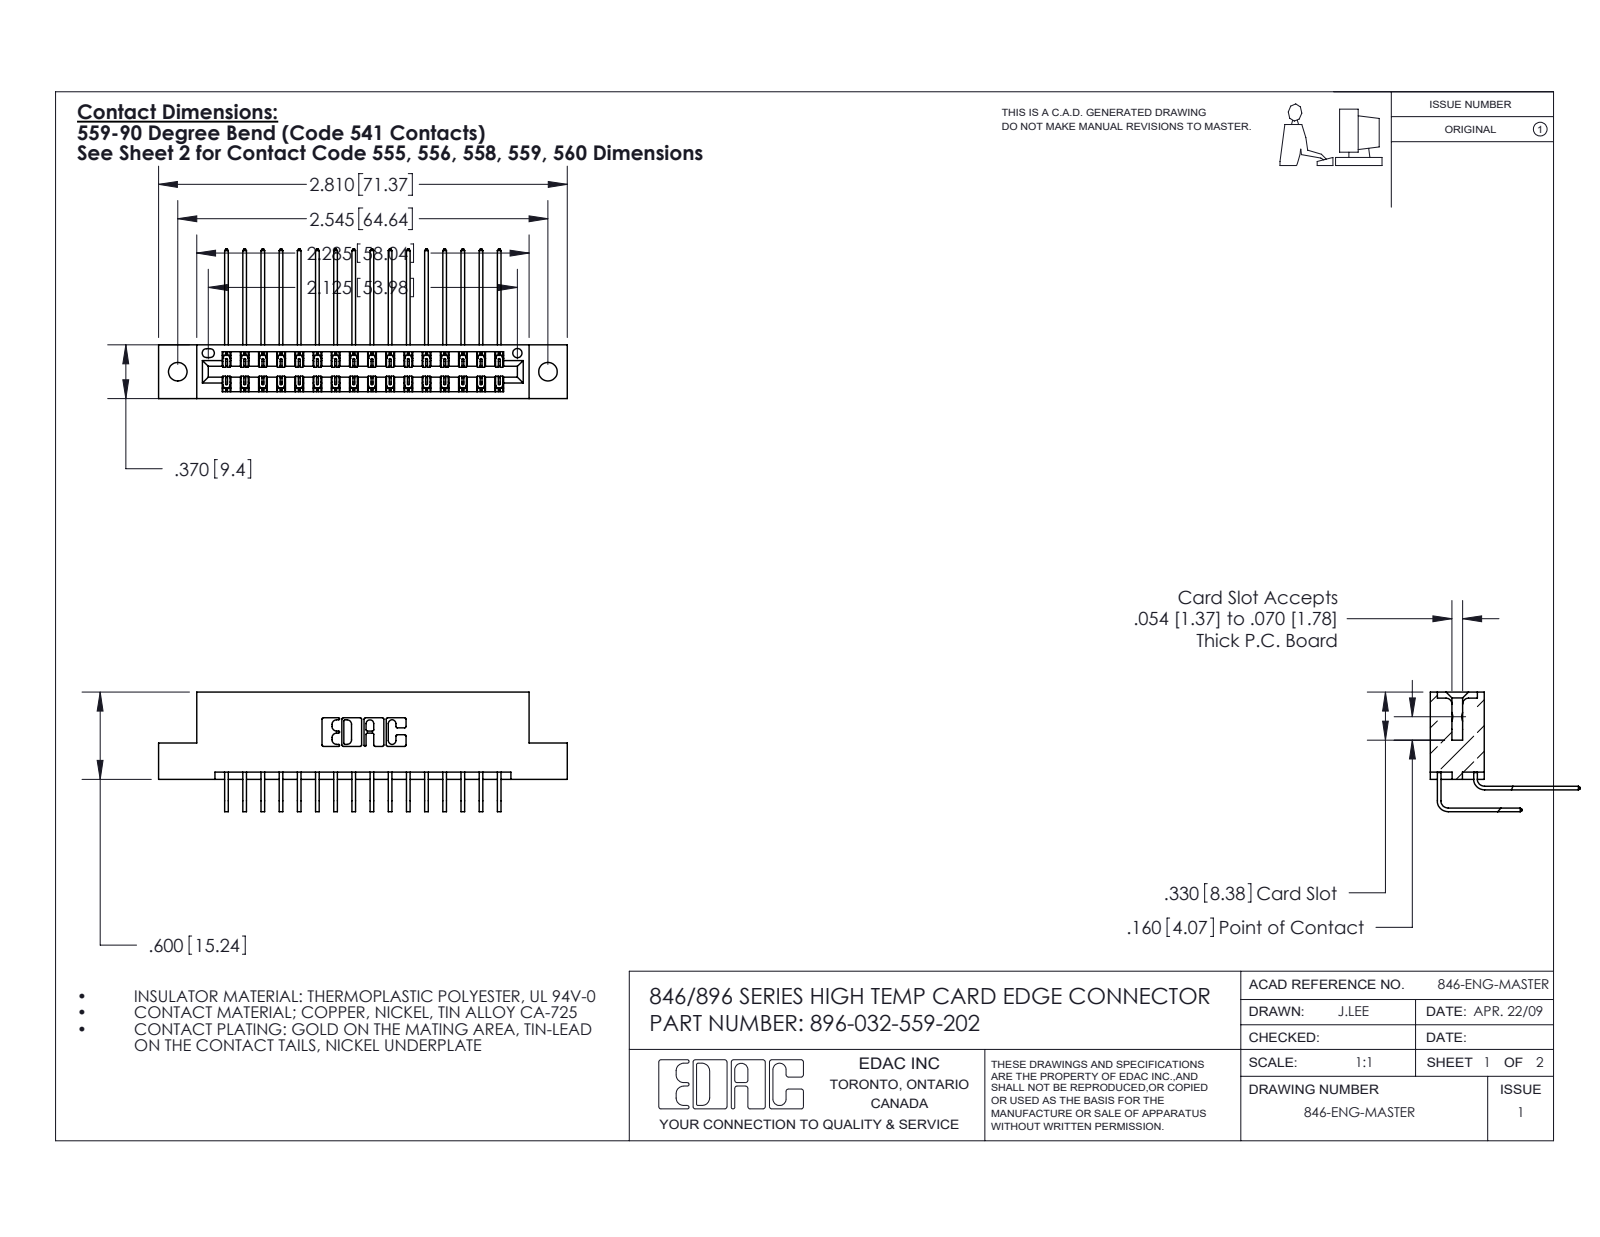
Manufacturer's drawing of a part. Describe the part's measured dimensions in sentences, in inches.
The part is named "396-032-559-202; 345-292-001_559 Tail - 2; 346 Part_Flush Mounting Lugs - 0.128 Dia; 345-292-001_558 559 Tail - 1". Its 3-D file was written by "SolidWorks 2016 (CONFIG_CONTROL_DESIGN)". It is 33 solids with 1850 faces: 1260 planar, 590 cylindrical and 0 other. Overall it measures 2.81 by 1.03 by 0.823 inches. Its volume is 0.421 cubic inches and its surface area 15.04 square inches. Round holes: 2 of diameter 0.128, 1 of diameter 0.064. Partial cylindrical surfaces (rounded edges, fillets, slot ends): 48 of radius 0.006, 22 of radius 0.01, 6 of radius 0.007, 6 of radius 0.031, 3 of radius 0.026, 2 of radius 0.014, 2 of radius 0.022, 2 of radius 0.024. The main face-to-face distances are 0.048, 0.322, 0.25, 0.025, 0.37, 0.072, 0.298, 0.275, 0.148, 0.222. The hole center spacings are 0.246, 2.338, 2.545.
